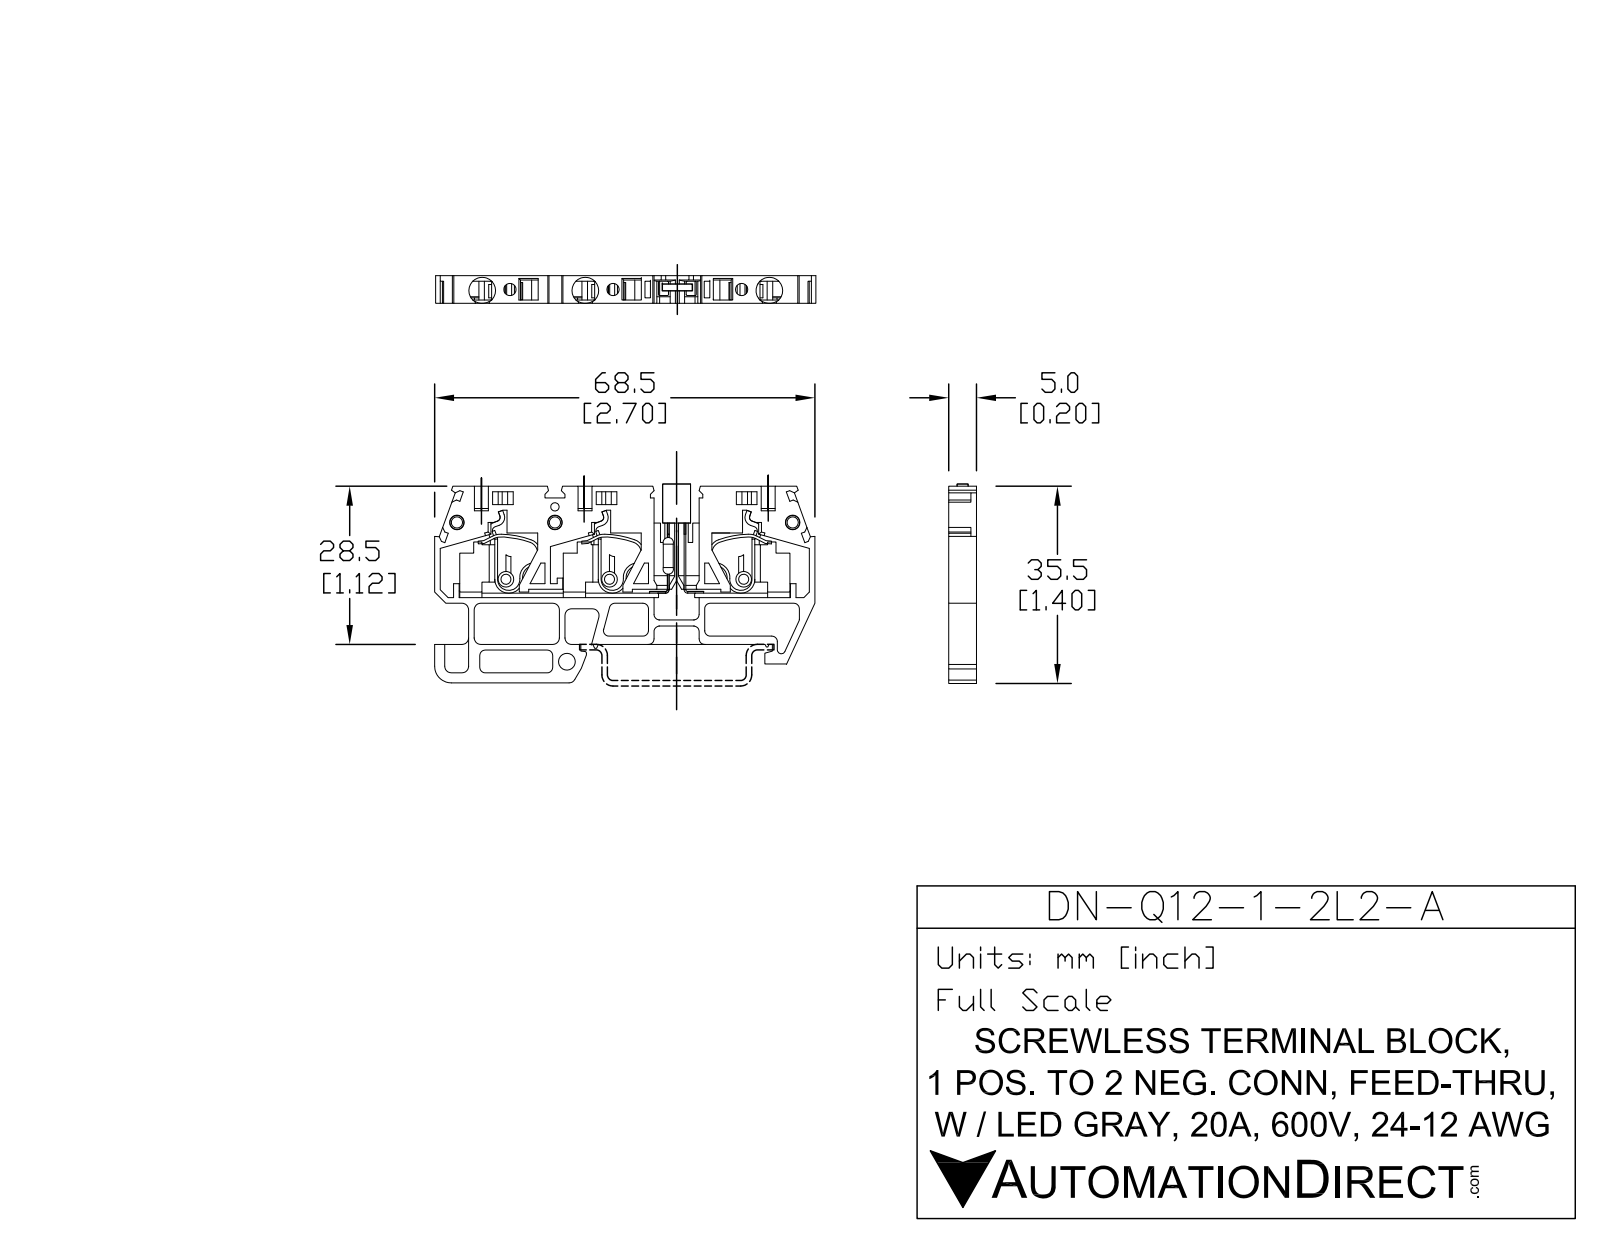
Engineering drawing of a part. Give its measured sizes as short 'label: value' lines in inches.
name: 20631_Piega1 D8; 42413D6_DN-Q12-1-2DR-A; 42413D9_DN-Q12-1-2L2-A; 20634 D8_20634 LN
written by: SolidWorks 2013 (AUTOMOTIVE_DESIGN)
unit: in
bodies: 5 solids, 415 faces (297 planar, 86 cylindrical, 32 other)
size: 2.701 × 1.409 × 0.232
volume: 0.4 in³; area: 11.21 in²
holes: 3× ⌀0.087, 3× ⌀0.102, 3× ⌀0.189, 1× ⌀0.059, 1× ⌀0.118
bosses: 4× ⌀0.012, 1× ⌀0.071
rounds: 19× R0.039, 12× R0.047, 1× R0.012, 1× R0.028, 1× R0.118
face distances: 0.197, 0.039, 0.079, 0.193, 0.118, 0.331, 0.028, 0.059, 0.047, 0.114
hole spacings: 0.197, 0.732, 1.11, 1.843, 0.11, 0.535, 0.693, 0.702
